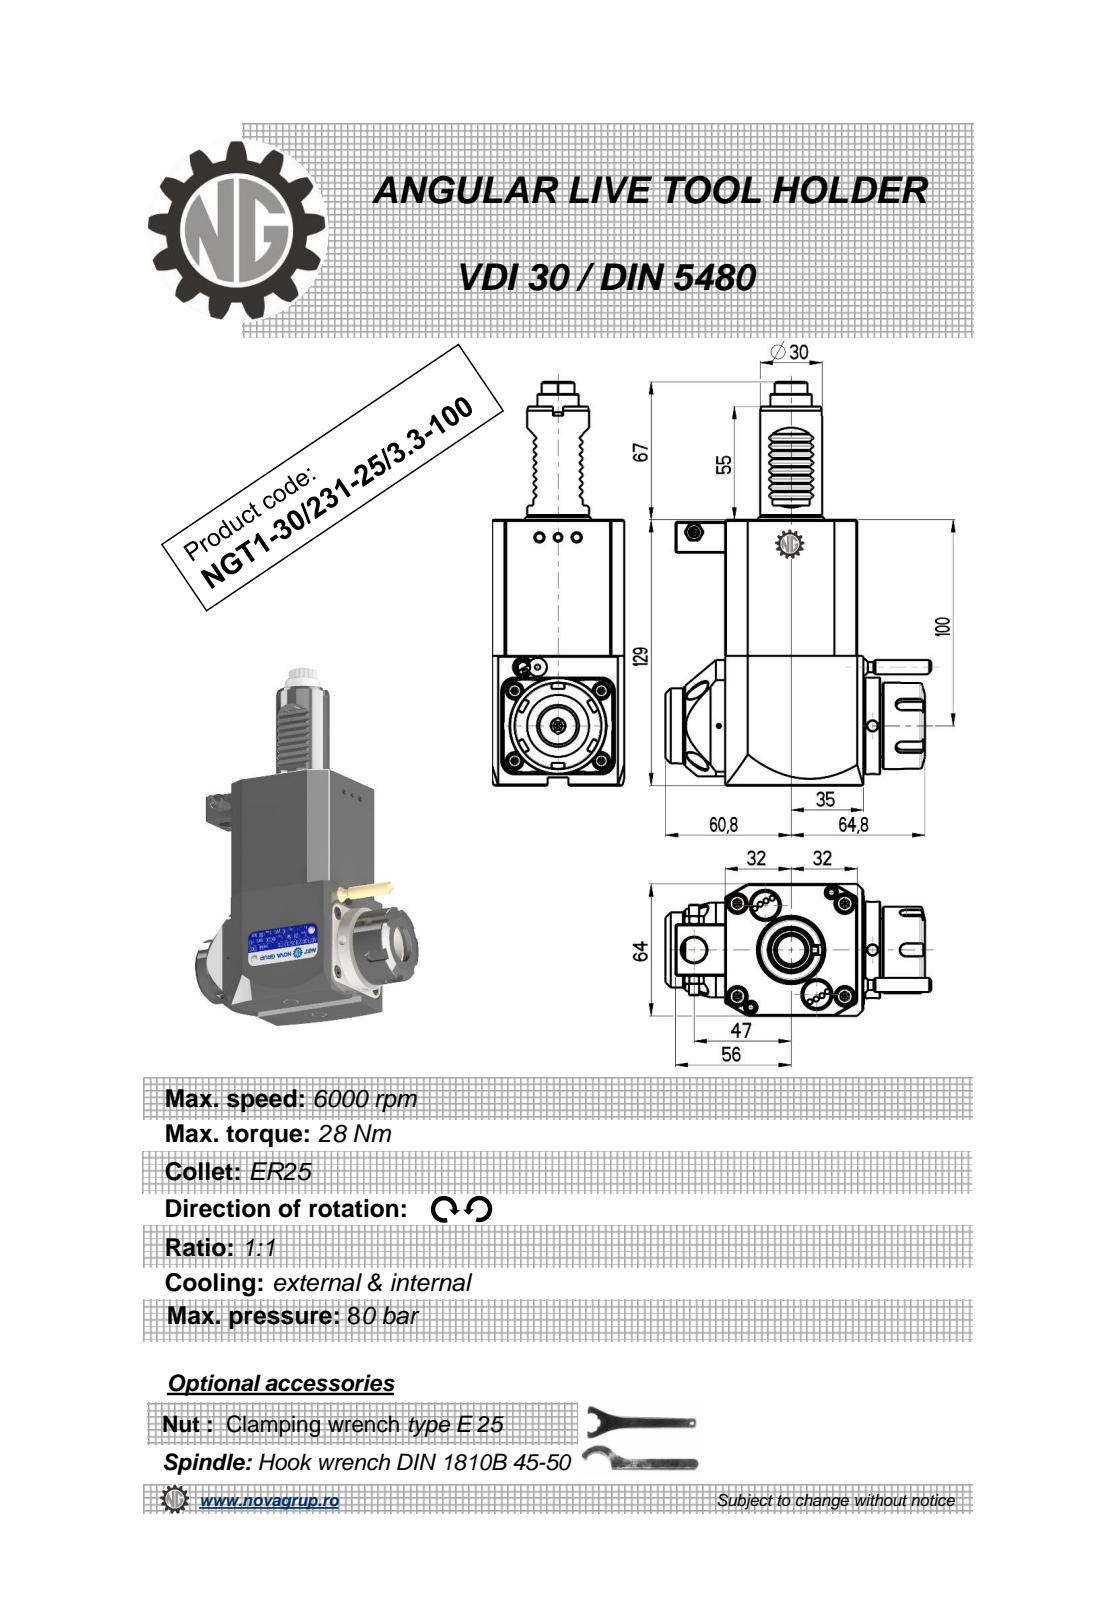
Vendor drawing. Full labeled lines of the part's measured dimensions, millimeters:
Part name (STEP PRODUCT): NGT1_30_231_25_3_3_100
STEP written by: PRO/ENGINEER BY PARAMETRIC TECHNOLOGY CORPORATION, 2010280 (CONFIG_CONTROL_DESIGN)
Units: millimetres
Bodies: 1 solid, 557 faces (224 planar, 163 cylindrical, 170 other)
Overall size (bounding box): 196 × 128.63 × 64
Volume: 656 679 mm³ · Surface area: 60 589 mm²
Round holes (diameter × count): ⌀5 ×2, ⌀2.5 ×1, ⌀3 ×1, ⌀4.2 ×1, ⌀9.5 ×1, ⌀12 ×1, ⌀20.3 ×1
Round bosses / shafts (diameter × count): ⌀8.96 ×2, ⌀5 ×2, ⌀47 ×1, ⌀42 ×1, ⌀36.5 ×1, ⌀35 ×1, ⌀30 ×1, ⌀20 ×1
Partial cylindrical surfaces — rounded edges, fillets, slot ends (radius × count): R1.98 ×36, R0.3 ×16, R0.26 ×12, R3 ×5, R160 ×2, R7.08 ×1, R7.92 ×1, R13 ×1
Main face-to-face distances: 64, 129, 76.42, 0.5, 67.2, 3.2, 67, 7.5, 3, 2.83
Hole centre spacings: 33.19, 65.25, 86.45, 91.5, 127.71
